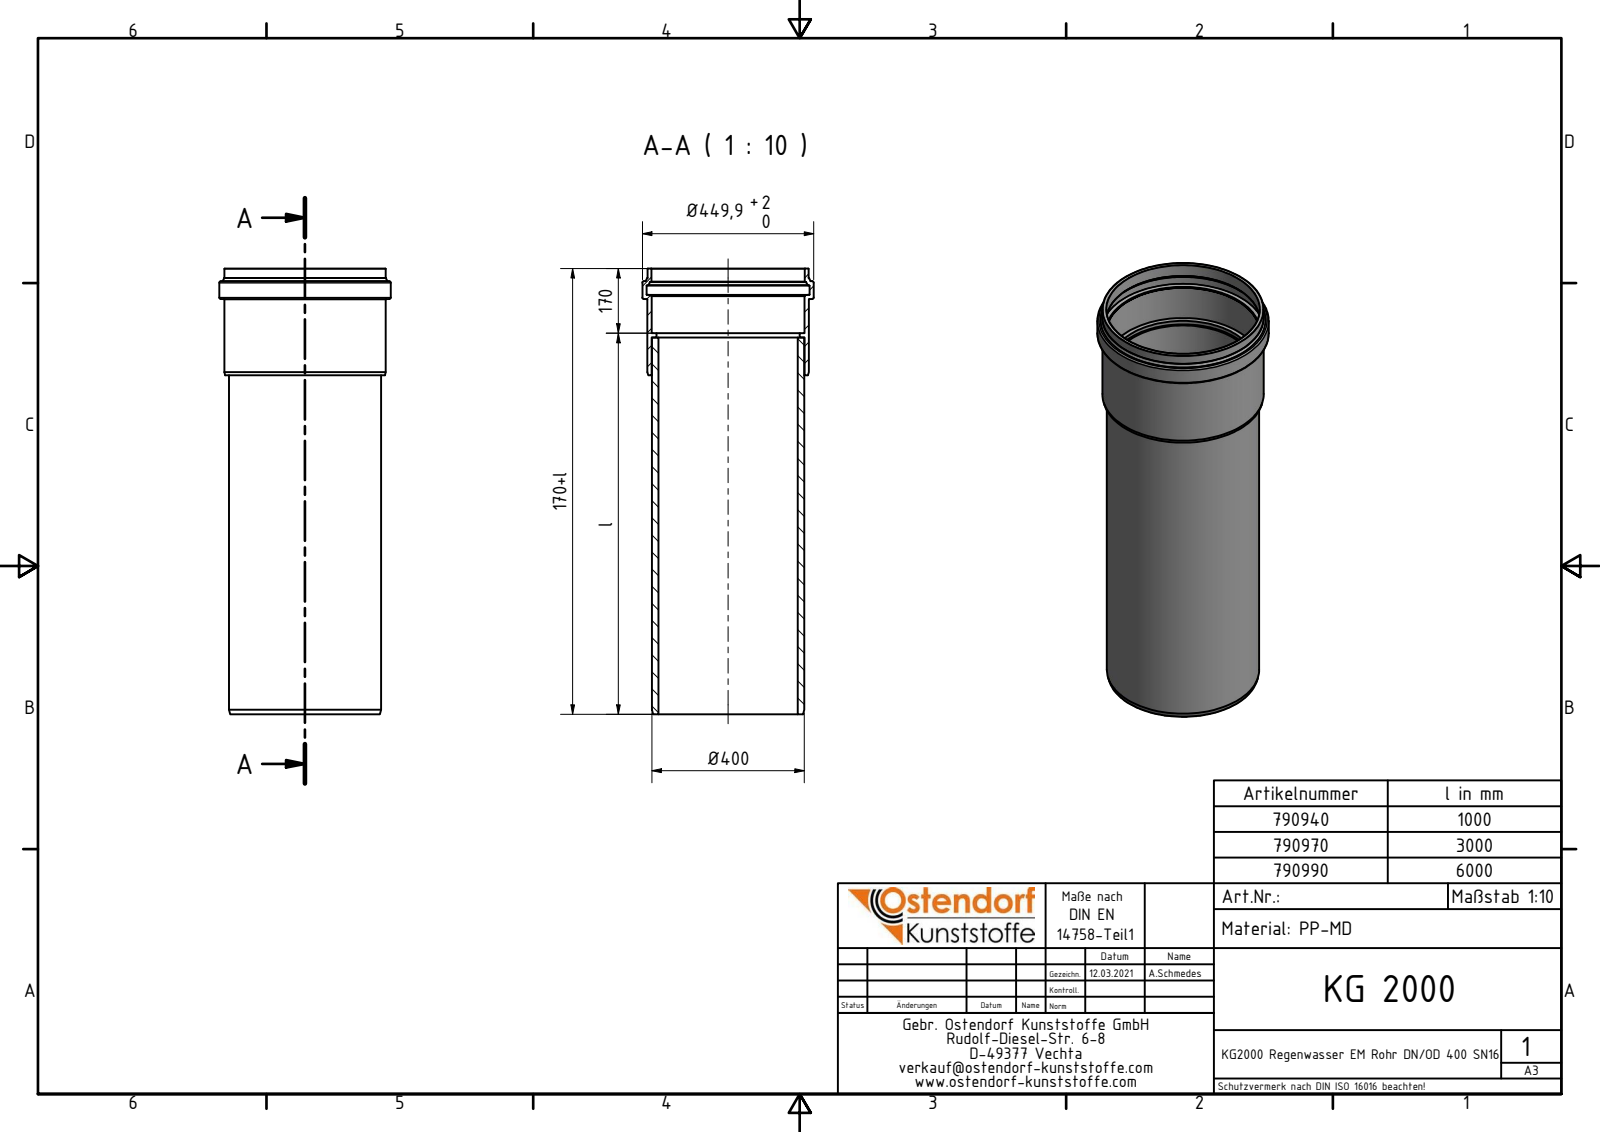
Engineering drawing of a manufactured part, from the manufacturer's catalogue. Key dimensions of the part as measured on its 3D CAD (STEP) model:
Part name (STEP PRODUCT): 790970 KG2000EM Rohr-Passlängen Regenwasser DN_OD 400x3000 SN16 Zusammenbau; 790970 KG2000EM Rohr-Passlängen Regenwasser DN_OD 400x3000 Teil 1 SN16; 790970 KG2000EM Rohr-Passlängen Regenwasser DN_OD 400x3000 Teil 2 SN16
STEP written by: Autodesk Inventor 2020 (AUTOMOTIVE_DESIGN)
Units: millimetres
Bodies: 2 solids, 41 faces (9 planar, 11 cylindrical, 21 other)
Overall size (bounding box): 3170 × 449.9 × 449.9
Volume: 65 970 000 mm³ · Surface area: 8 066 000 mm²
Round holes (diameter × count): ⌀365.8 ×1, ⌀376 ×1, ⌀401.7 ×1, ⌀402.1 ×1, ⌀427.7 ×1
Round bosses / shafts (diameter × count): ⌀449.9 ×1, ⌀423.9 ×1, ⌀423.06 ×1, ⌀400 ×1
Main face-to-face distances: 2988.9, 3000, 11.1, 2890, 98.9, 110, 3170, 280, 181.1, 170
